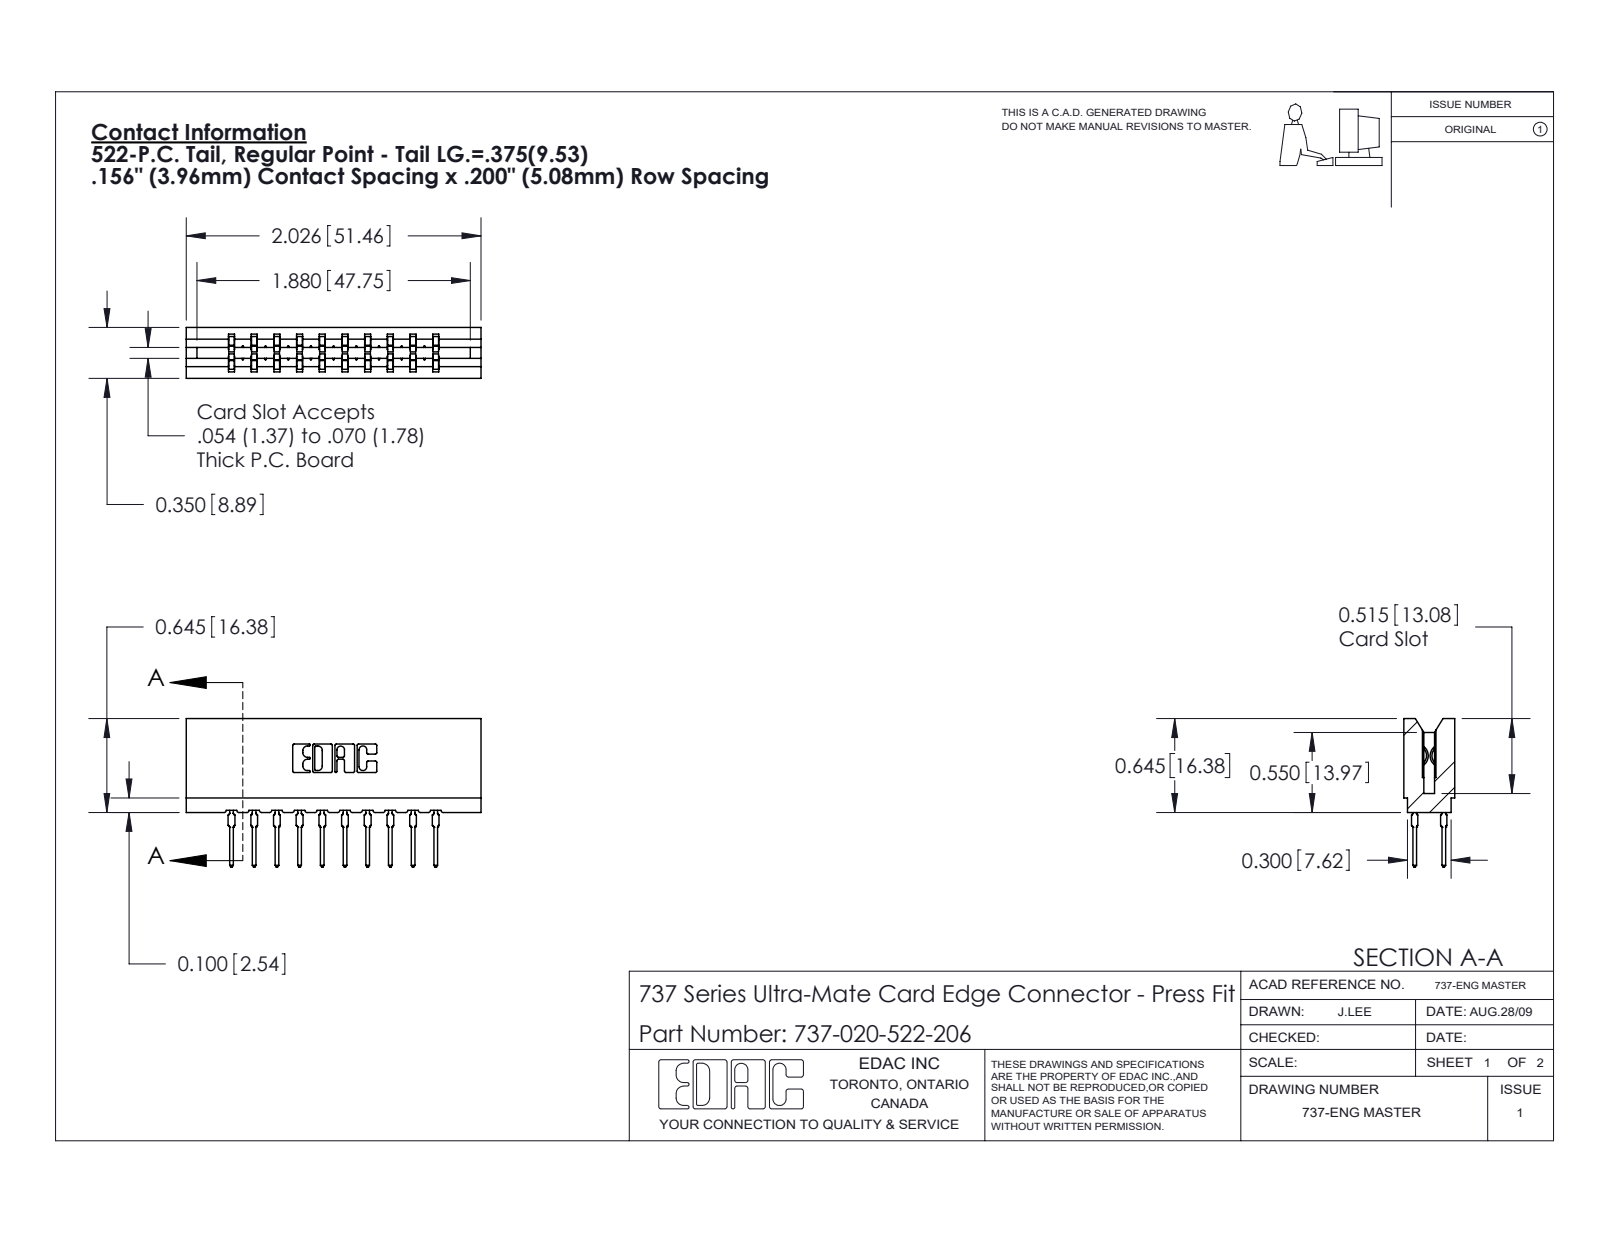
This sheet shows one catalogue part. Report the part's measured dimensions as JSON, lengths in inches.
{"part_name": "745-292-001_522; 737-020-522-206; 737 Part_Insulator Option - 06", "step_written_by": "SolidWorks 2020 (CONFIG_CONTROL_DESIGN)", "units": "inches", "bodies": {"solids": 21, "faces": 1895, "planar": 985, "cylindrical": 390, "other": 520}, "overall_size": [2.026, 1.021, 0.35], "volume_in3": 0.323, "surface_area_in2": 10.95, "partial_cylinders_radius": [[0.021, 40], [0.01, 22], [0.015, 20], [0.005, 8], [0.011, 8], [0.007, 6], [0.031, 6], [0.026, 3]], "face_to_face_distances": [0.156, 0.138, 0.212, 0.35, 0.624, 0.312, 0.354, 0.78, 0.468, 0.51]}
